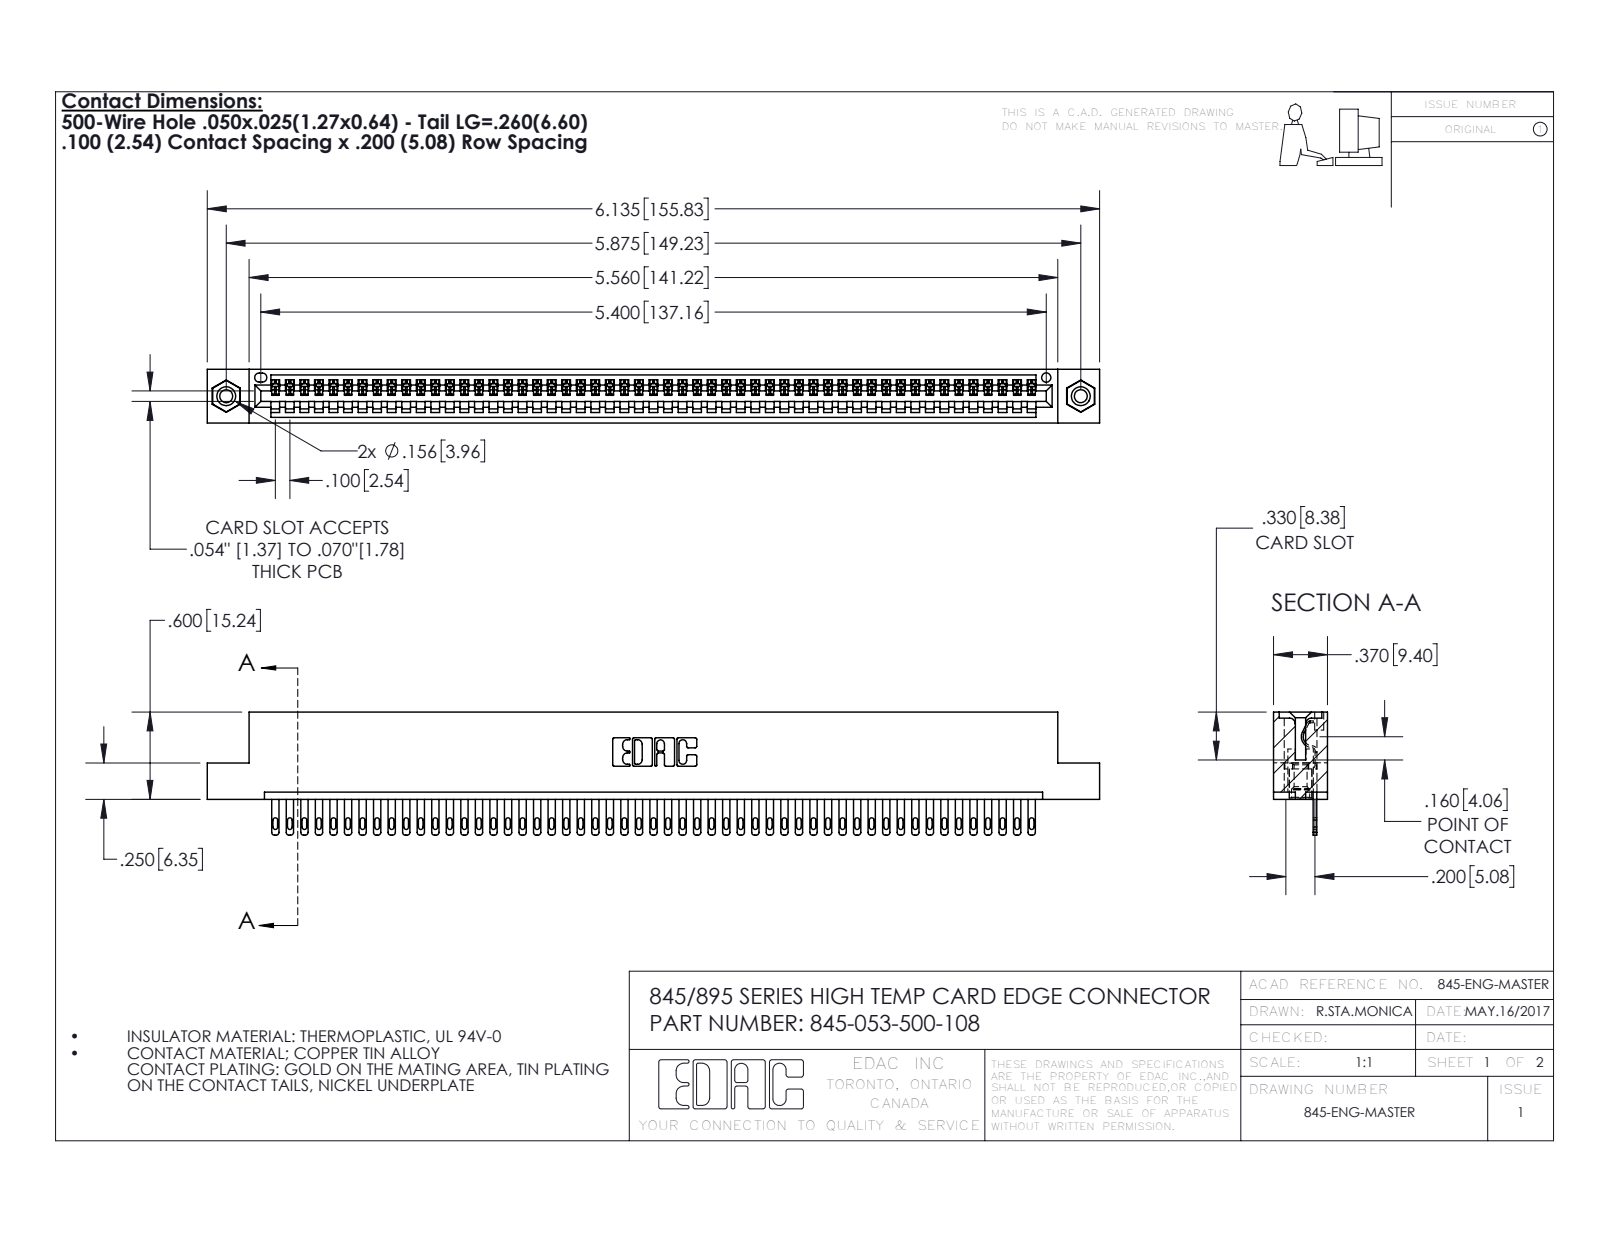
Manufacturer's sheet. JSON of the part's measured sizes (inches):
{"part_name": "345 Part_Flush Mounting Lugs - 0.156 Dia-TI; 345-292-001_345-293-100; 345-053-500-108; 345-250-001_345-250-003-102", "step_written_by": "SolidWorks 2016 (CONFIG_CONTROL_DESIGN)", "units": "inches", "bodies": {"solids": 56, "faces": 3048, "planar": 1914, "cylindrical": 1118, "other": 16}, "overall_size": [6.135, 0.847, 0.37], "volume_in3": 0.91, "surface_area_in2": 31.17, "round_holes": [[0.089, 2], [0.125, 2], [0.156, 2], [0.064, 1]], "round_bosses_or_shafts": [[0.155, 2]], "partial_cylinders_radius": [[0.006, 106], [0.016, 106], [0.02, 106], [0.01, 22], [0.007, 6], [0.031, 6], [0.026, 3], [0.031, 2]], "face_to_face_distances": [0.072, 0.298, 0.37, 0.098, 0.272, 0.025, 0.2, 0.225, 0.149, 0.072], "hole_center_spacings": [0.27, 5.639, 5.875]}
